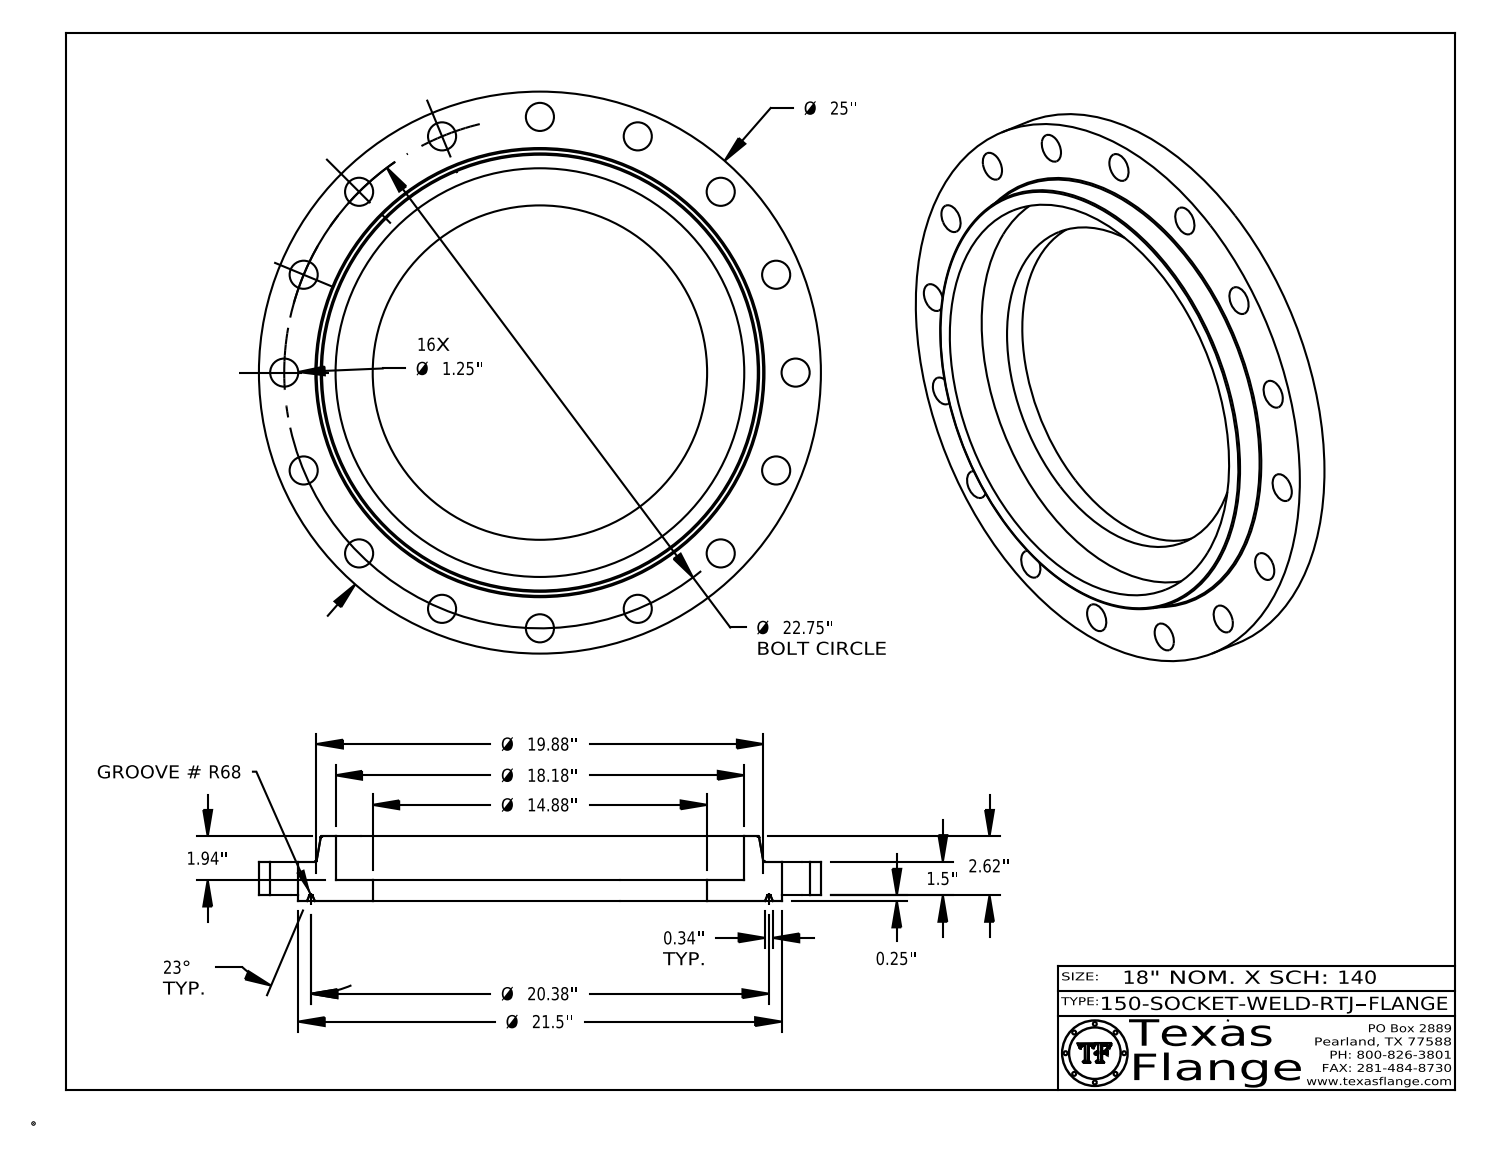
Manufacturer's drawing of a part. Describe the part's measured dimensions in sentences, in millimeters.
The part is named "150-SOCKET-WELD-RTJ". Its 3-D file was written by "CATIA V5 STEP AP214 (AUTOMOTIVE_DESIGN)". It is 1 solid with 446 faces: 372 planar, 60 cylindrical and 14 other. Overall it measures 635 by 635 by 72.9 millimeters. Its volume is 7 692 000 cubic millimeters and its surface area 680 600 square millimeters. Round holes: 16 of diameter 31.8, 1 of diameter 12.6, 1 of diameter 377.9, 1 of diameter 461.8. Round bosses or shafts: 8 of diameter 0.8, 1 of diameter 635, 1 of diameter 546.1, 1 of diameter 9.9. The main face-to-face distances are 44.5, 6.4, 38.1, 23.6, 17.3, 20.8, 72.9, 66.5, 49.3, 28.4. The hole center spacings are 321, 566.8, 288.9, 221.1, 408.6, 533.9, 112.7, 112.8.
